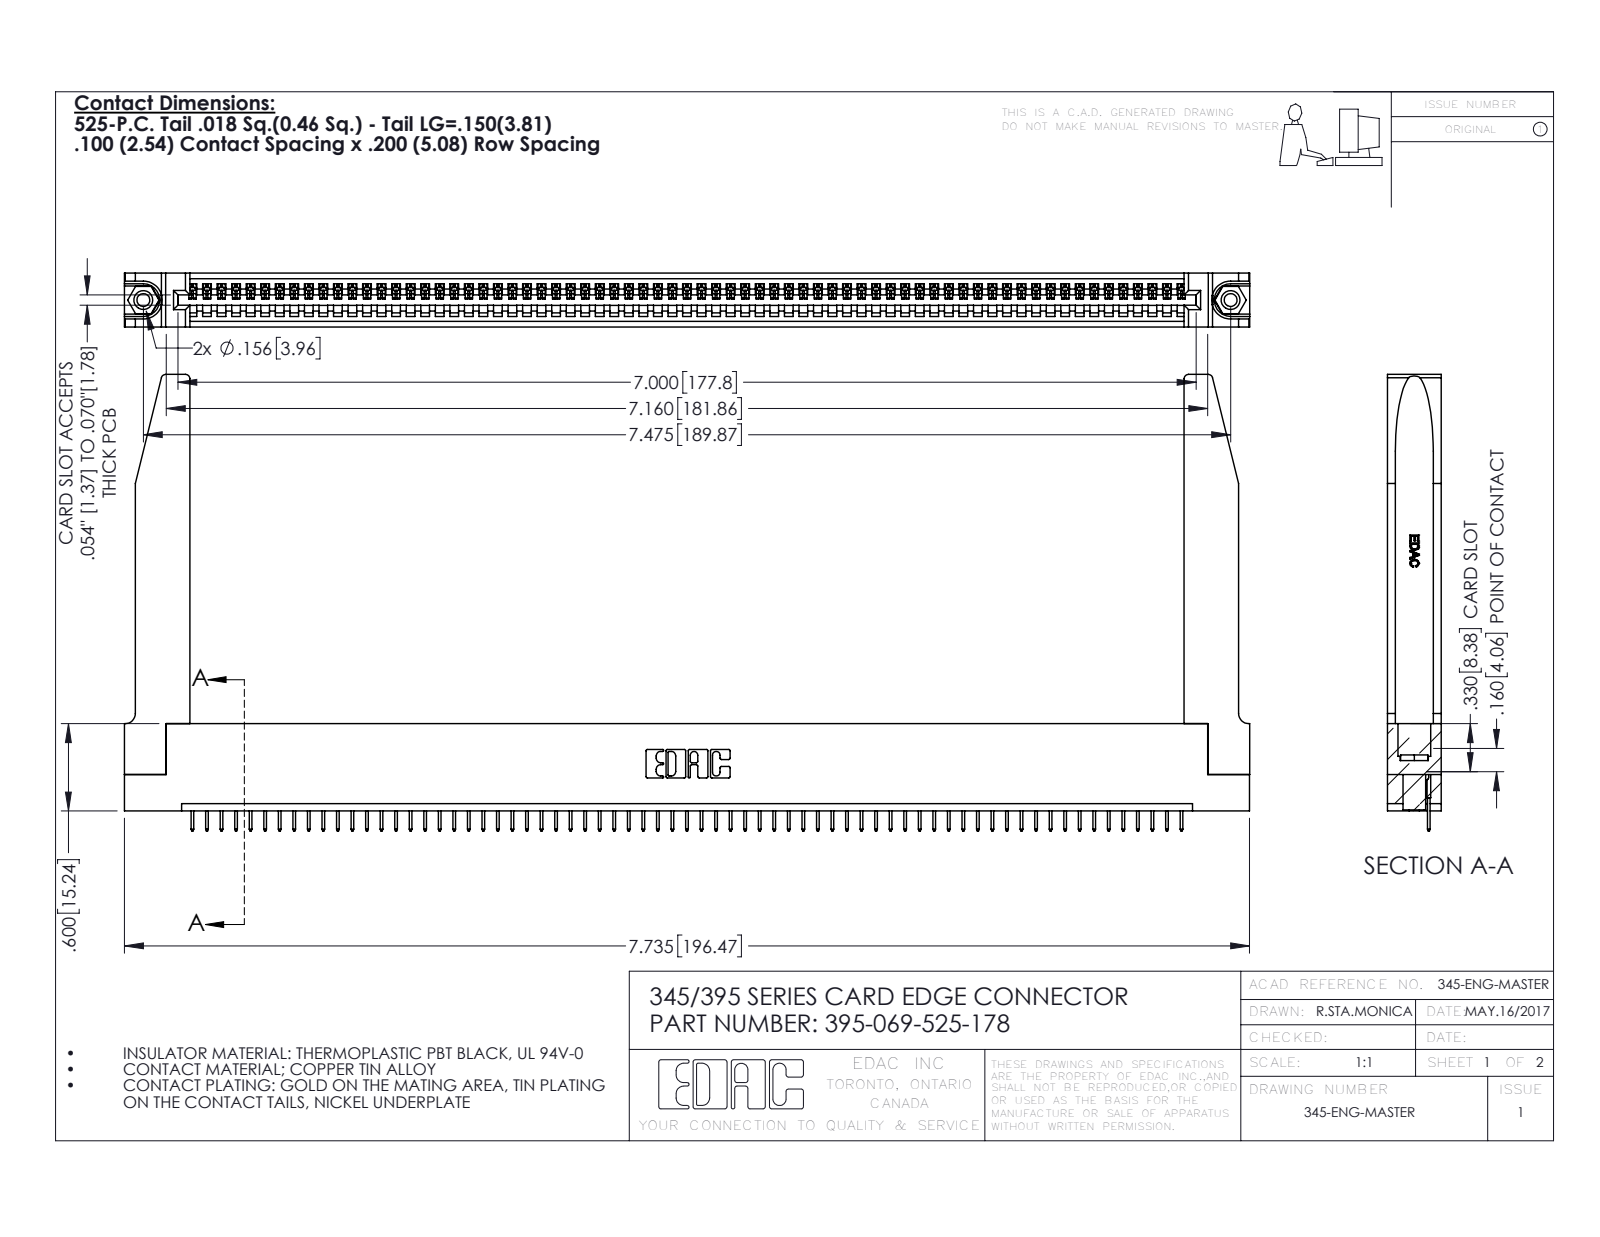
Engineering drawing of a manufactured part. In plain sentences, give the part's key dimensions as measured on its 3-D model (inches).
The part is named "345-292-001_345-293-125; 345-250-001_345-250-001-102; 345 Part_Flush Mounting Lugs - 0.156 Dia-TH; 395-069-525-178 (+1 more)". Its 3-D file was written by "SolidWorks 2020 (CONFIG_CONTROL_DESIGN)". It is 74 solids with 4638 faces: 3396 planar, 1190 cylindrical and 52 other. Overall it measures 7.736 by 3.137 by 0.37 inches. Its volume is 1.609 cubic inches and its surface area 48.04 square inches. Round holes: 2 of diameter 0.089, 2 of diameter 0.125, 2 of diameter 0.156, 1 of diameter 0.064. Round bosses or shafts: 2 of diameter 0.155. Partial cylindrical surfaces (rounded edges, fillets, slot ends): 138 of radius 0.006, 22 of radius 0.01, 8 of radius 0.03, 6 of radius 0.007, 6 of radius 0.031, 3 of radius 0.026, 2 of radius 0.031, 2 of radius 0.04. The main face-to-face distances are 0.37, 0.072, 0.298, 0.2, 0.098, 0.272, 0.025, 0.225, 0.072, 0.149. The hole center spacings are 0.27, 7.239, 7.475.
